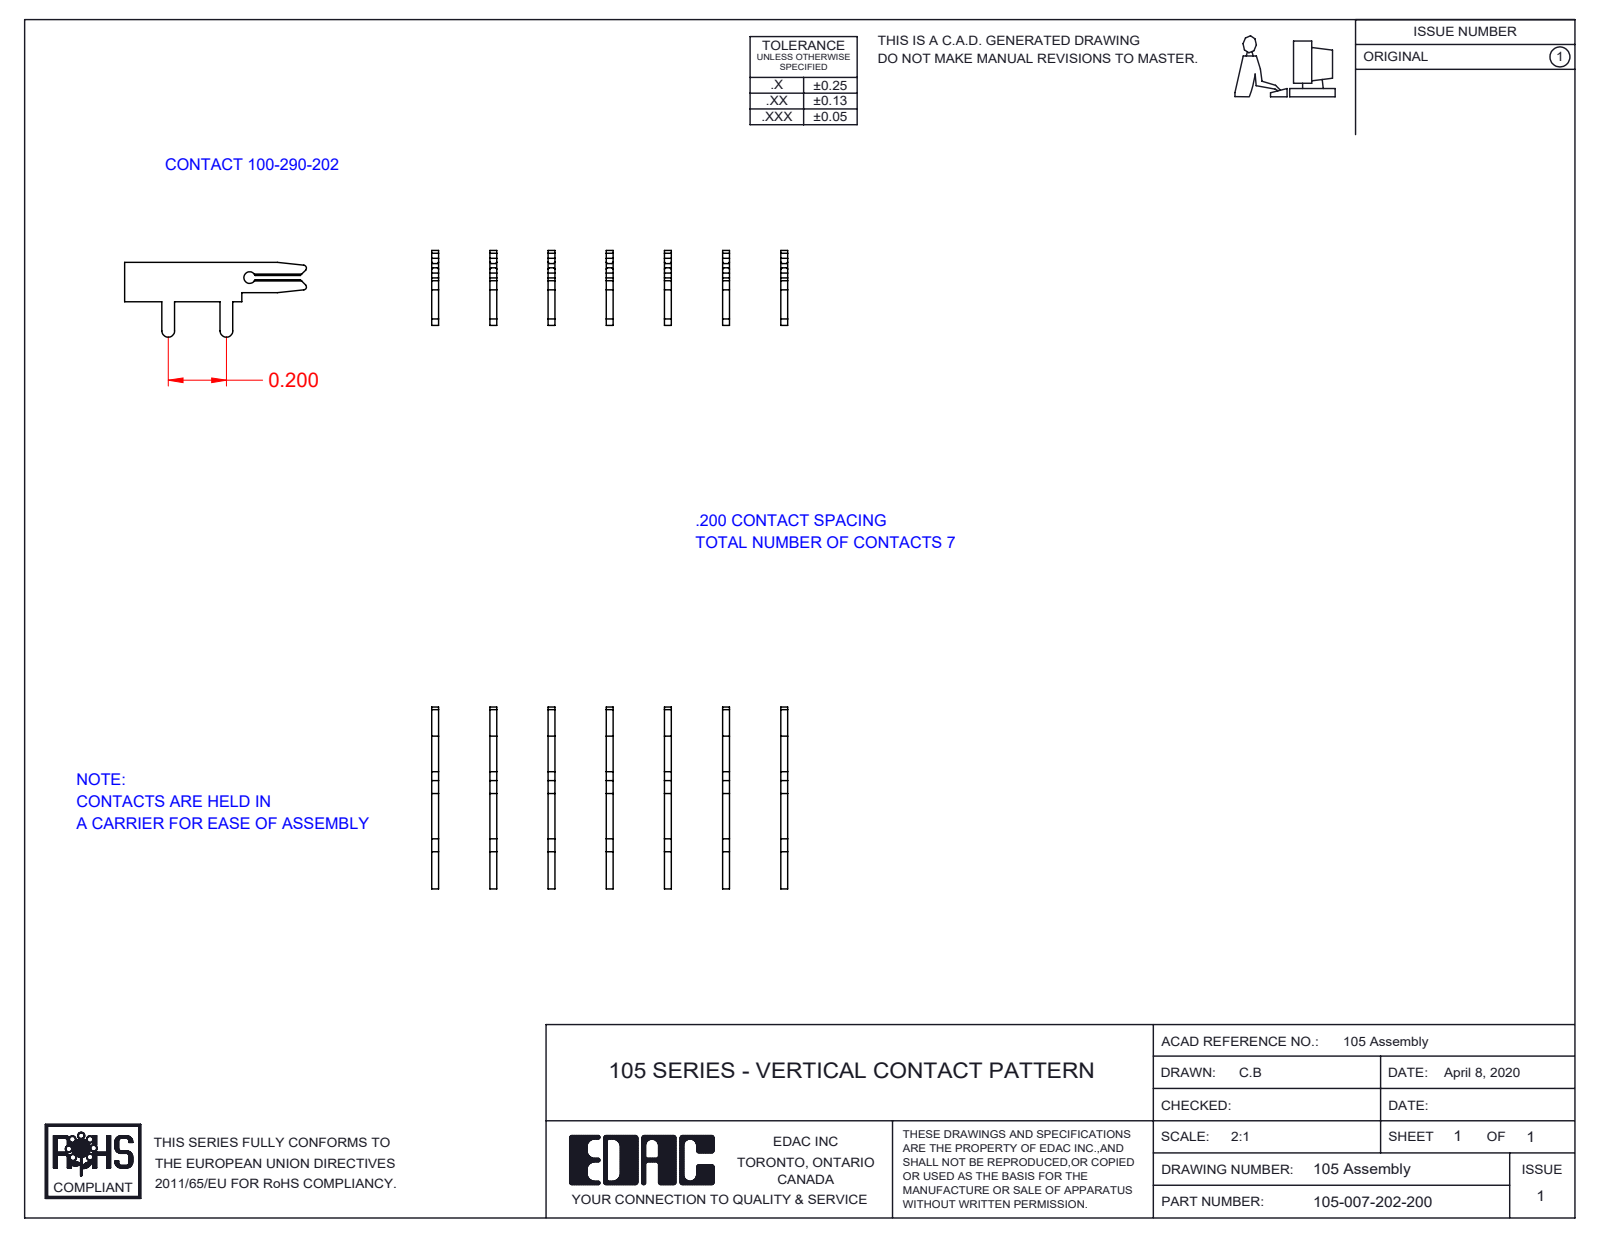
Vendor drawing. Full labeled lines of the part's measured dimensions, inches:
Part name (STEP PRODUCT): 105-007-202-200; 100-290-001_100-290-202
STEP written by: SolidWorks 2016 (CONFIG_CONTROL_DESIGN)
Units: inches
Bodies: 7 solids, 210 faces (161 planar, 49 cylindrical, 0 other)
Overall size (bounding box): 1.224 × 0.625 × 0.257
Volume: 0.014 in³ · Surface area: 1.533 in²
Round holes (diameter × count): ⌀0.04 ×1
Partial cylindrical surfaces — rounded edges, fillets, slot ends (radius × count): R0.01 ×2, R0.022 ×2
Main face-to-face distances: 0.2, 0.4, 0.6, 0.024, 0.8, 0.224, 0.176, 0.424, 0.376, 1
